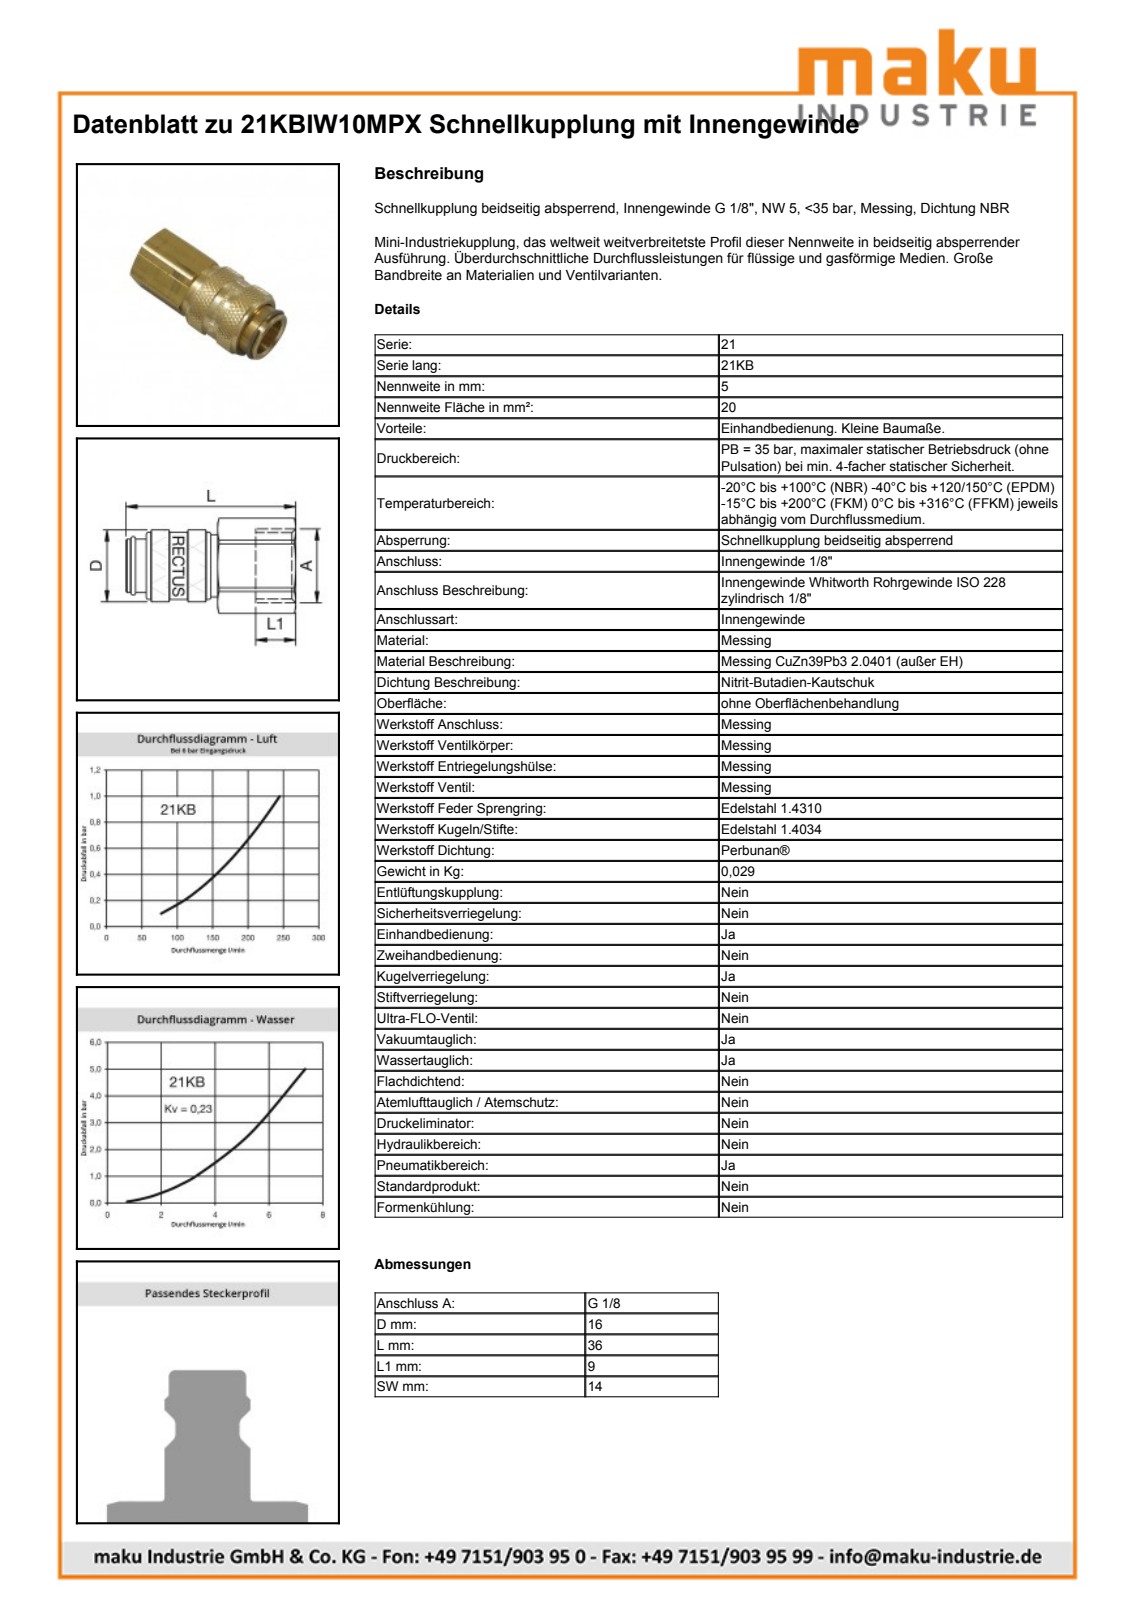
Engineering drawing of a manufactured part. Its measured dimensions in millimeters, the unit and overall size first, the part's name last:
Units: millimetres
Overall size (bounding box): 36.15 × 16.15 × 16.15
Round holes (diameter × count): ⌀8.57 ×1, ⌀11.46 ×1, ⌀12.15 ×1, ⌀14 ×1
Round bosses / shafts (diameter × count): ⌀16.15 ×1, ⌀15.1 ×1, ⌀12 ×1, ⌀11.4 ×1, ⌀11.29 ×1, ⌀11.15 ×1
Partial cylindrical surfaces — rounded edges, fillets, slot ends (radius × count): R7.45 ×1, R7.9 ×1
Main face-to-face distances: 14, 27.15, 36.15, 9, 16.15, 11, 20, 4.56, 11.59, 22.59
Volume: 5 353 mm³ · Surface area: 3 754 mm²
Bodies: 2 solids, 456 faces (149 planar, 62 cylindrical, 245 other)
Part name (STEP PRODUCT): D106832
STEP written by: Autodesk Inventor 2013 (AUTOMOTIVE_DESIGN)
